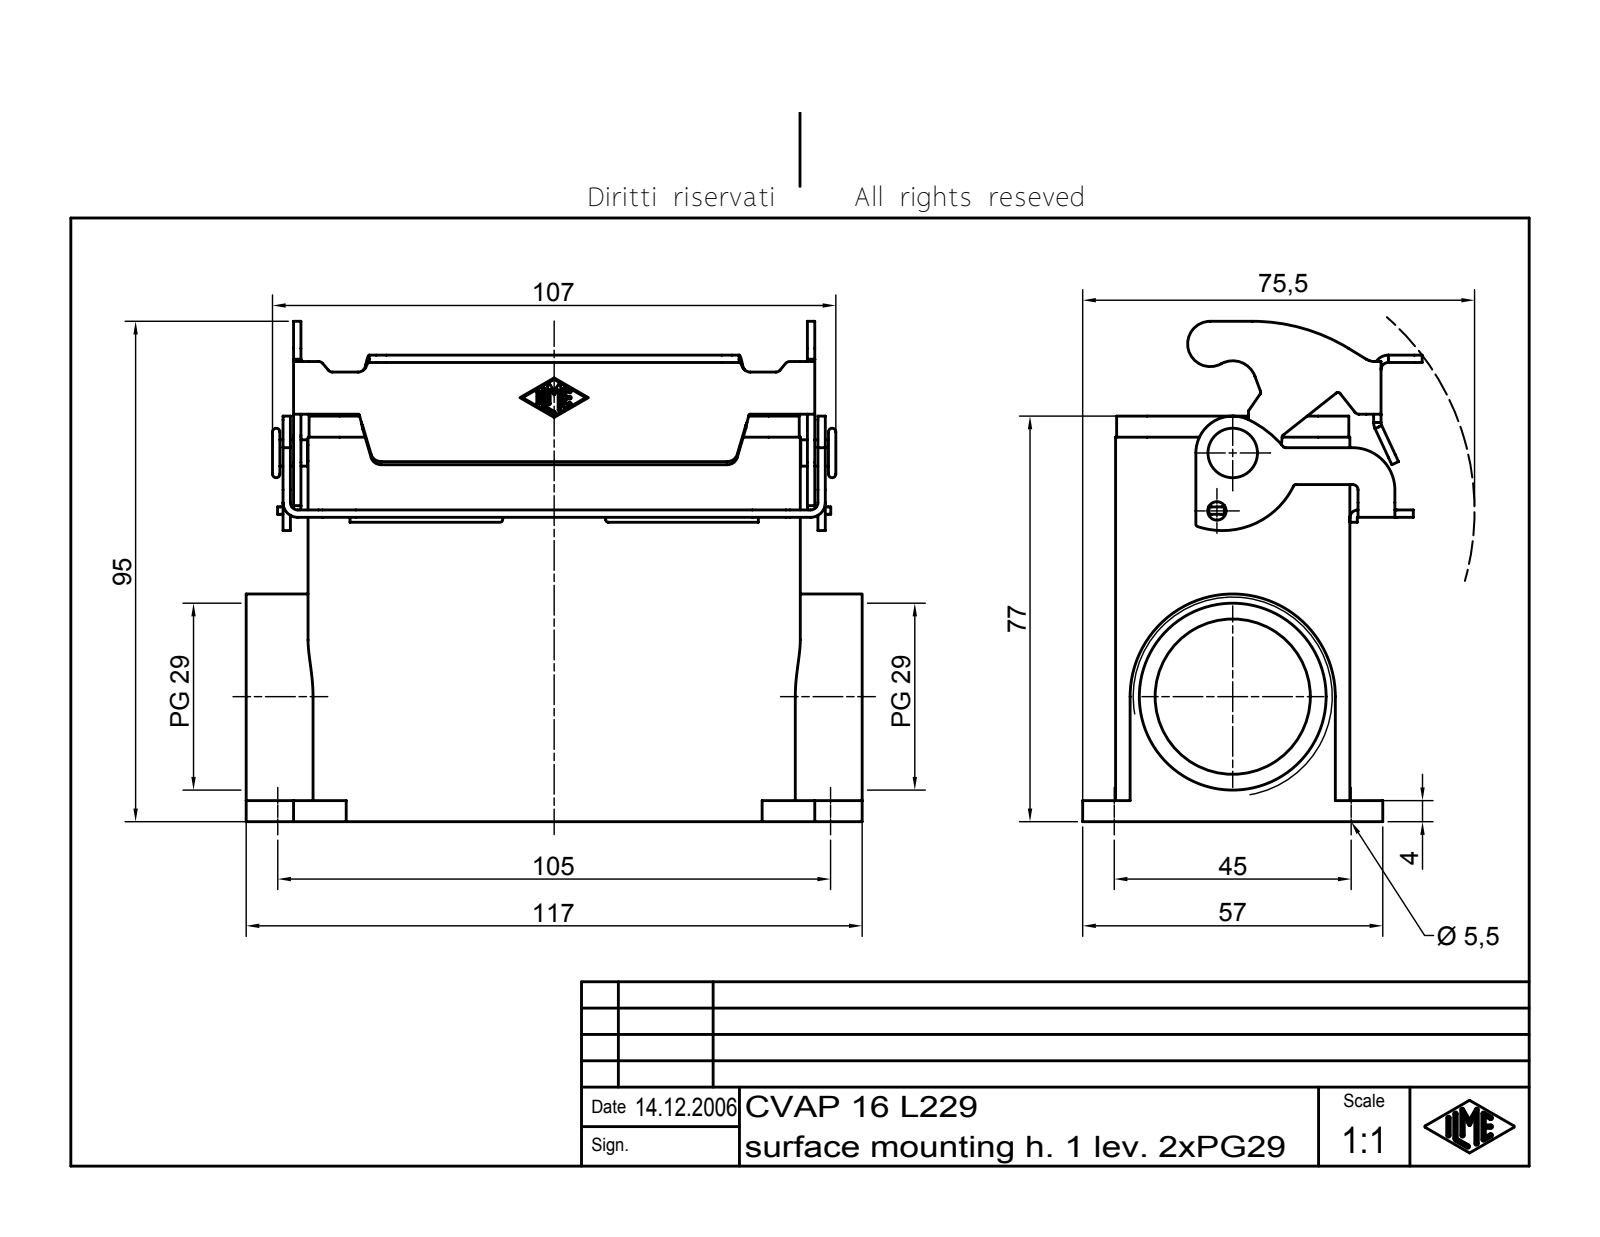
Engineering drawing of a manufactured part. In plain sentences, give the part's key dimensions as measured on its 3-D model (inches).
The part is named "CVAP 16 L229". Its 3-D file was written by "Autodesk Inventor 7 (AUTOMOTIVE_DESIGN)". It is 2 solids with 403 faces: 141 planar, 118 cylindrical and 144 other. Overall it measures 4.606 by 3.74 by 2.539 inches. Its volume is 7.582 cubic inches and its surface area 100.8 square inches. Round holes: 4 of diameter 0.217, 1 of diameter 0.138, 1 of diameter 1.161, 1 of diameter 1.397. Round bosses or shafts: 1 of diameter 0.197, 1 of diameter 0.126, 1 of diameter 0.118. Partial cylindrical surfaces (rounded edges, fillets, slot ends): 15 of radius 0.01, 9 of radius 0.02, 9 of radius 0.059, 8 of radius 0.039, 6 of radius 0.055, 6 of radius 0.079, 6 of radius 0.11, 4 of radius 0.071. The main face-to-face distances are 0.157, 1.594, 1.752, 1.437, 0.055, 0.453, 3.228, 1.587, 0.463, 0.915. The hole center spacings are 1.772, 4.134, 4.498, 1.393.
